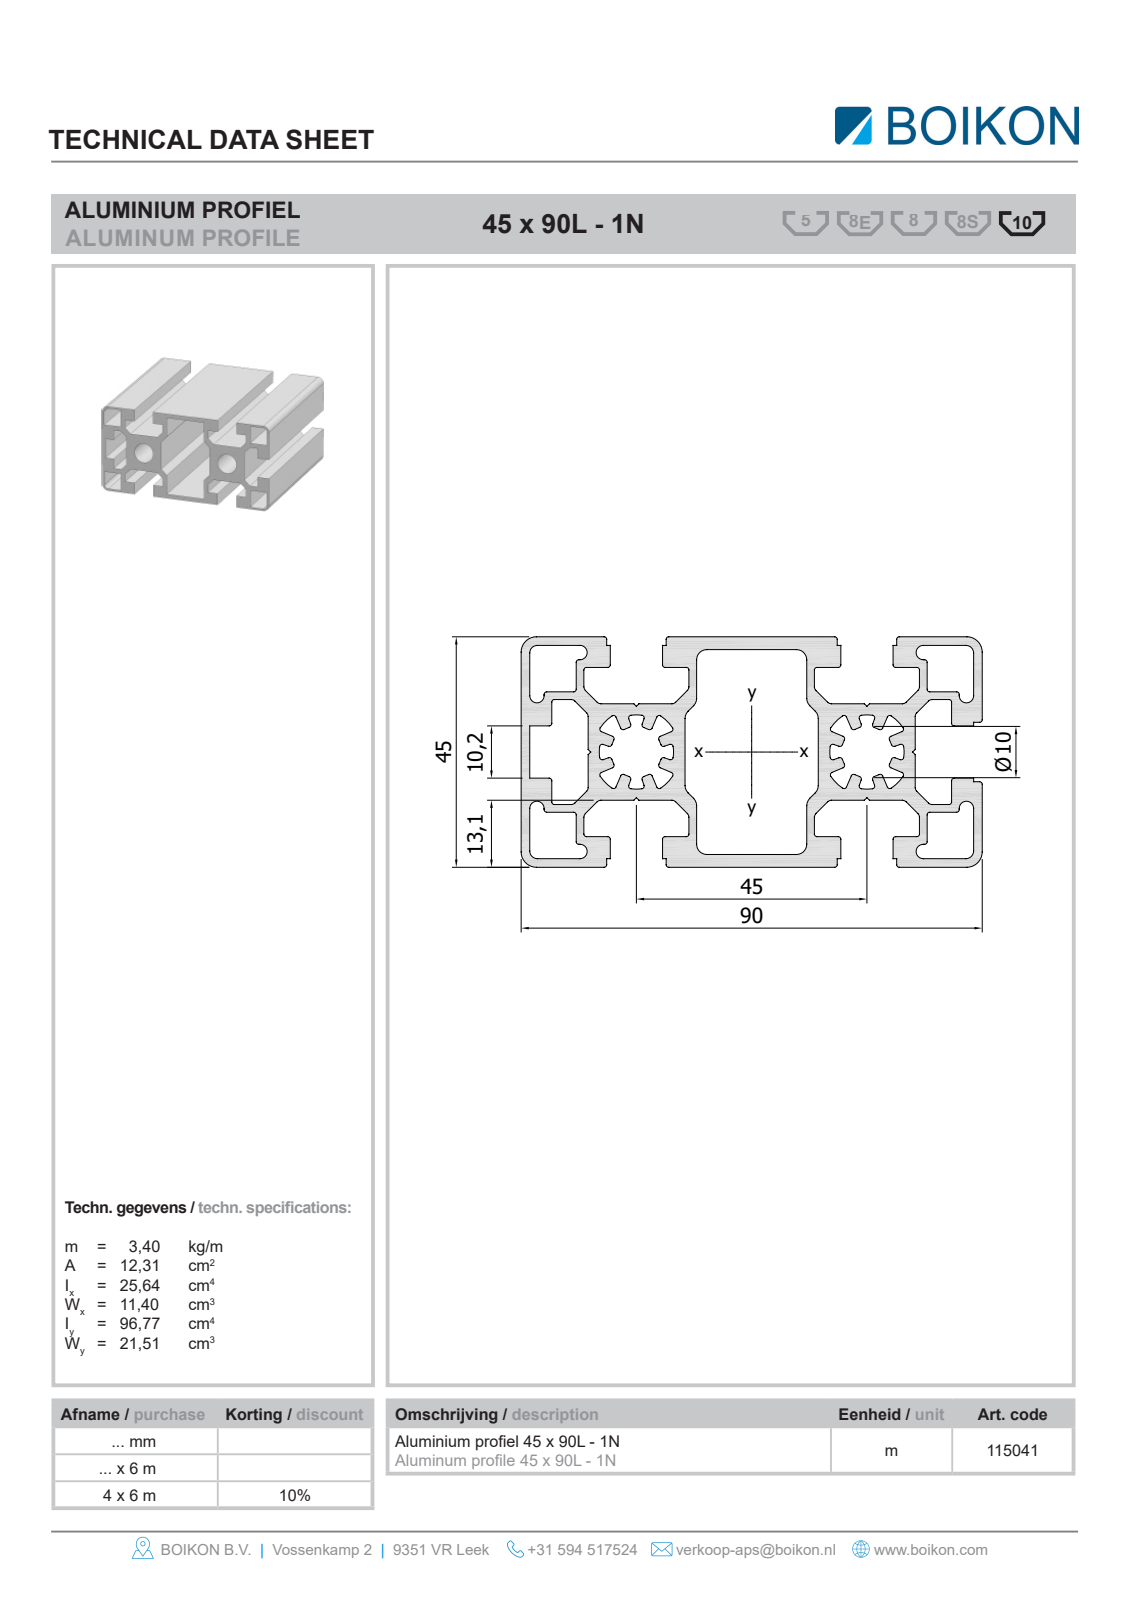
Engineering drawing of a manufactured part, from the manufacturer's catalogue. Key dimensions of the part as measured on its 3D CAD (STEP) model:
Part name (STEP PRODUCT): Root; 11504145x90L-1NBOIKON0
STEP written by: HiCAD 2013 1802.4 Build 509 (AUTOMOTIVE_DESIGN)
Units: millimetres
Bodies: 1 solid, 104 faces (94 planar, 10 cylindrical, 0 other)
Overall size (bounding box): 1000 × 90 × 45
Volume: 1 457 000 mm³ · Surface area: 876 485 mm²
Round holes (diameter × count): ⌀10.2 ×2
Partial cylindrical surfaces — rounded edges, fillets, slot ends (radius × count): R2 ×4, R3 ×4
Main face-to-face distances: 45, 13.1, 31.9, 10, 14.5, 4.3, 3.1, 21.9, 6, 7.1
Hole centre spacings: 45
